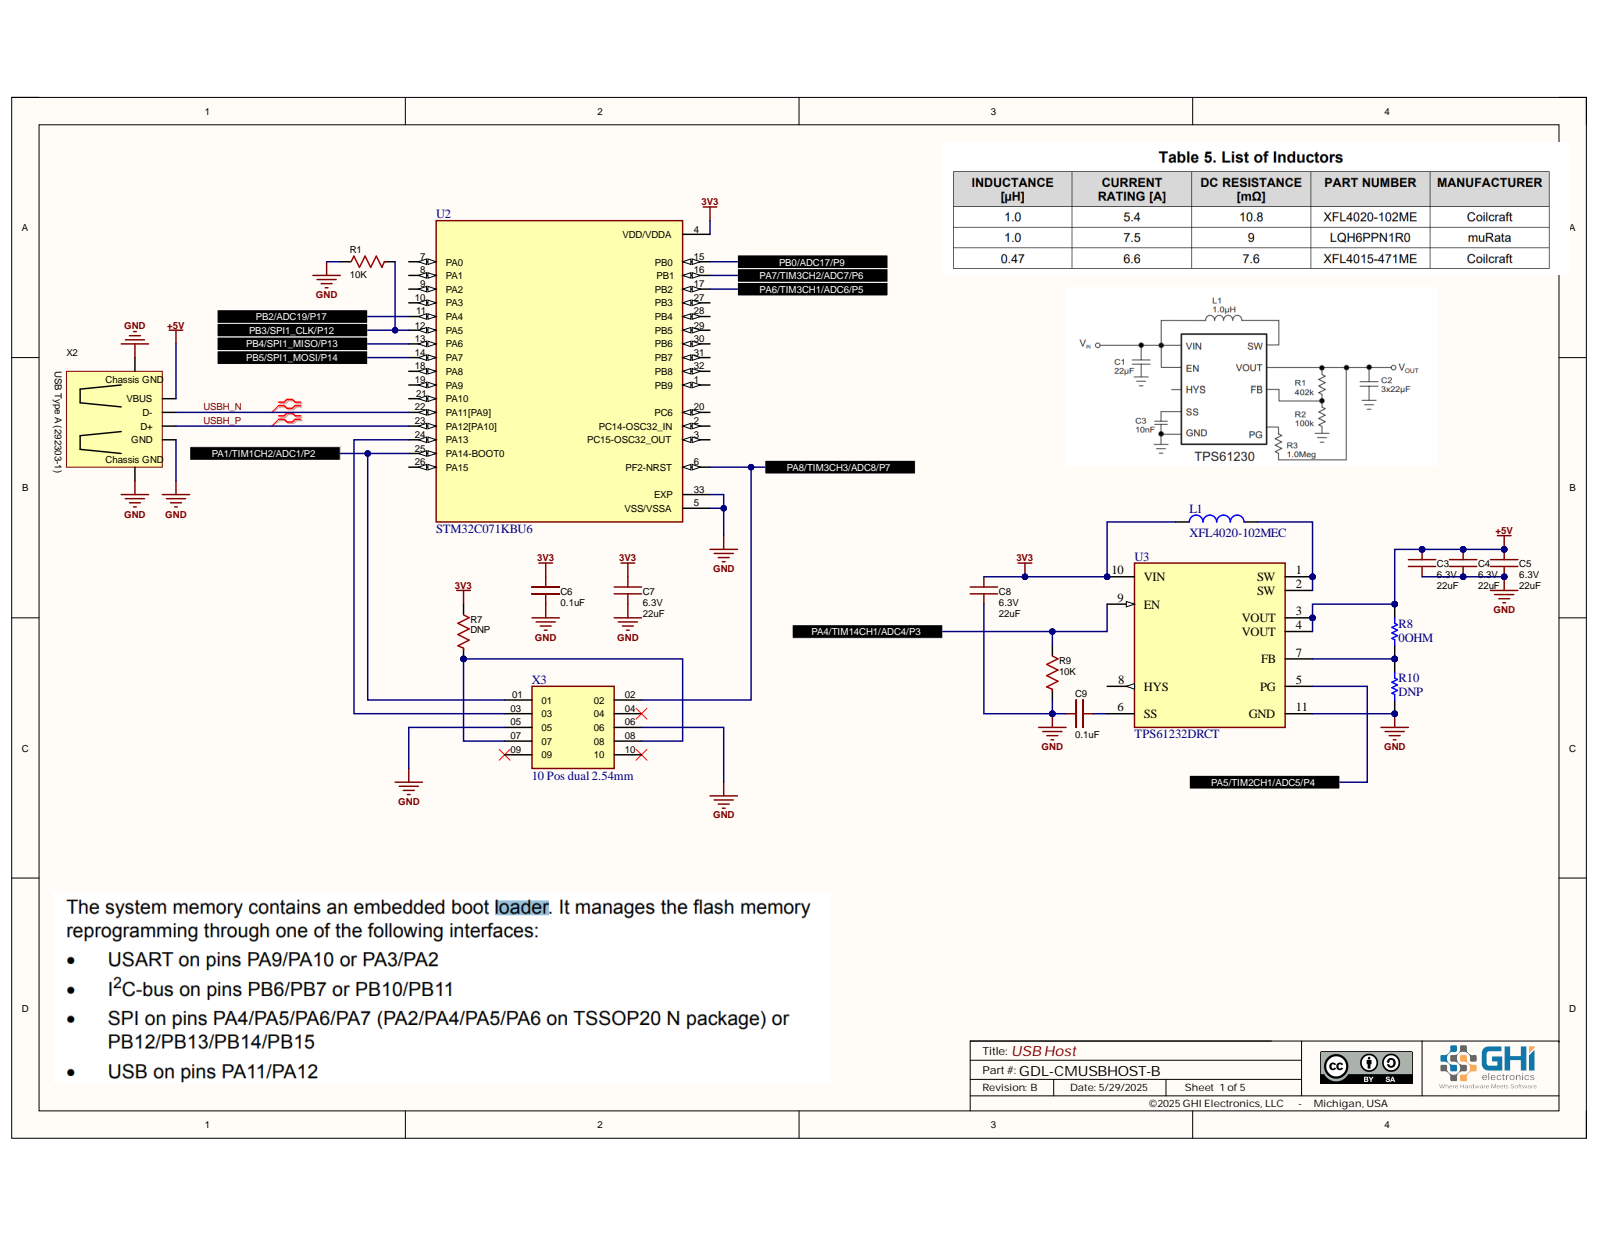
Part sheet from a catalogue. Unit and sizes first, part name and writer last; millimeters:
Units: millimetres
Overall size (bounding box): 37 × 34 × 11.37
Round holes (diameter × count): ⌀1 ×4, ⌀3 ×4, ⌀1.02 ×2, ⌀2.3 ×2
Partial cylindrical surfaces — rounded edges, fillets, slot ends (radius × count): R0.12 ×70, R0.15 ×66, R0.25 ×12, R0.3 ×12, R0.12 ×10, R0.13 ×8, R0.4 ×8, R0.32 ×6
Main face-to-face distances: 0.32, 0.45, 5.44, 6.63, 7.08, 6.88, 5.12, 1, 5.88, 0.68
Hole centre spacings: 2.5, 4.09, 4.5, 5.1, 6.19, 8.04, 8.43, 10.43
Volume: 1 057 mm³ · Surface area: 4 049 mm²
Bodies: 170 solids, 3409 faces (2159 planar, 622 cylindrical, 628 other)
Part name (STEP PRODUCT): PCB; Board; R1; User Library-R SMD 0402 (+7 more)
STEP written by: Open CASCADE 7.5 (AUTOMOTIVE_DESIGN)
